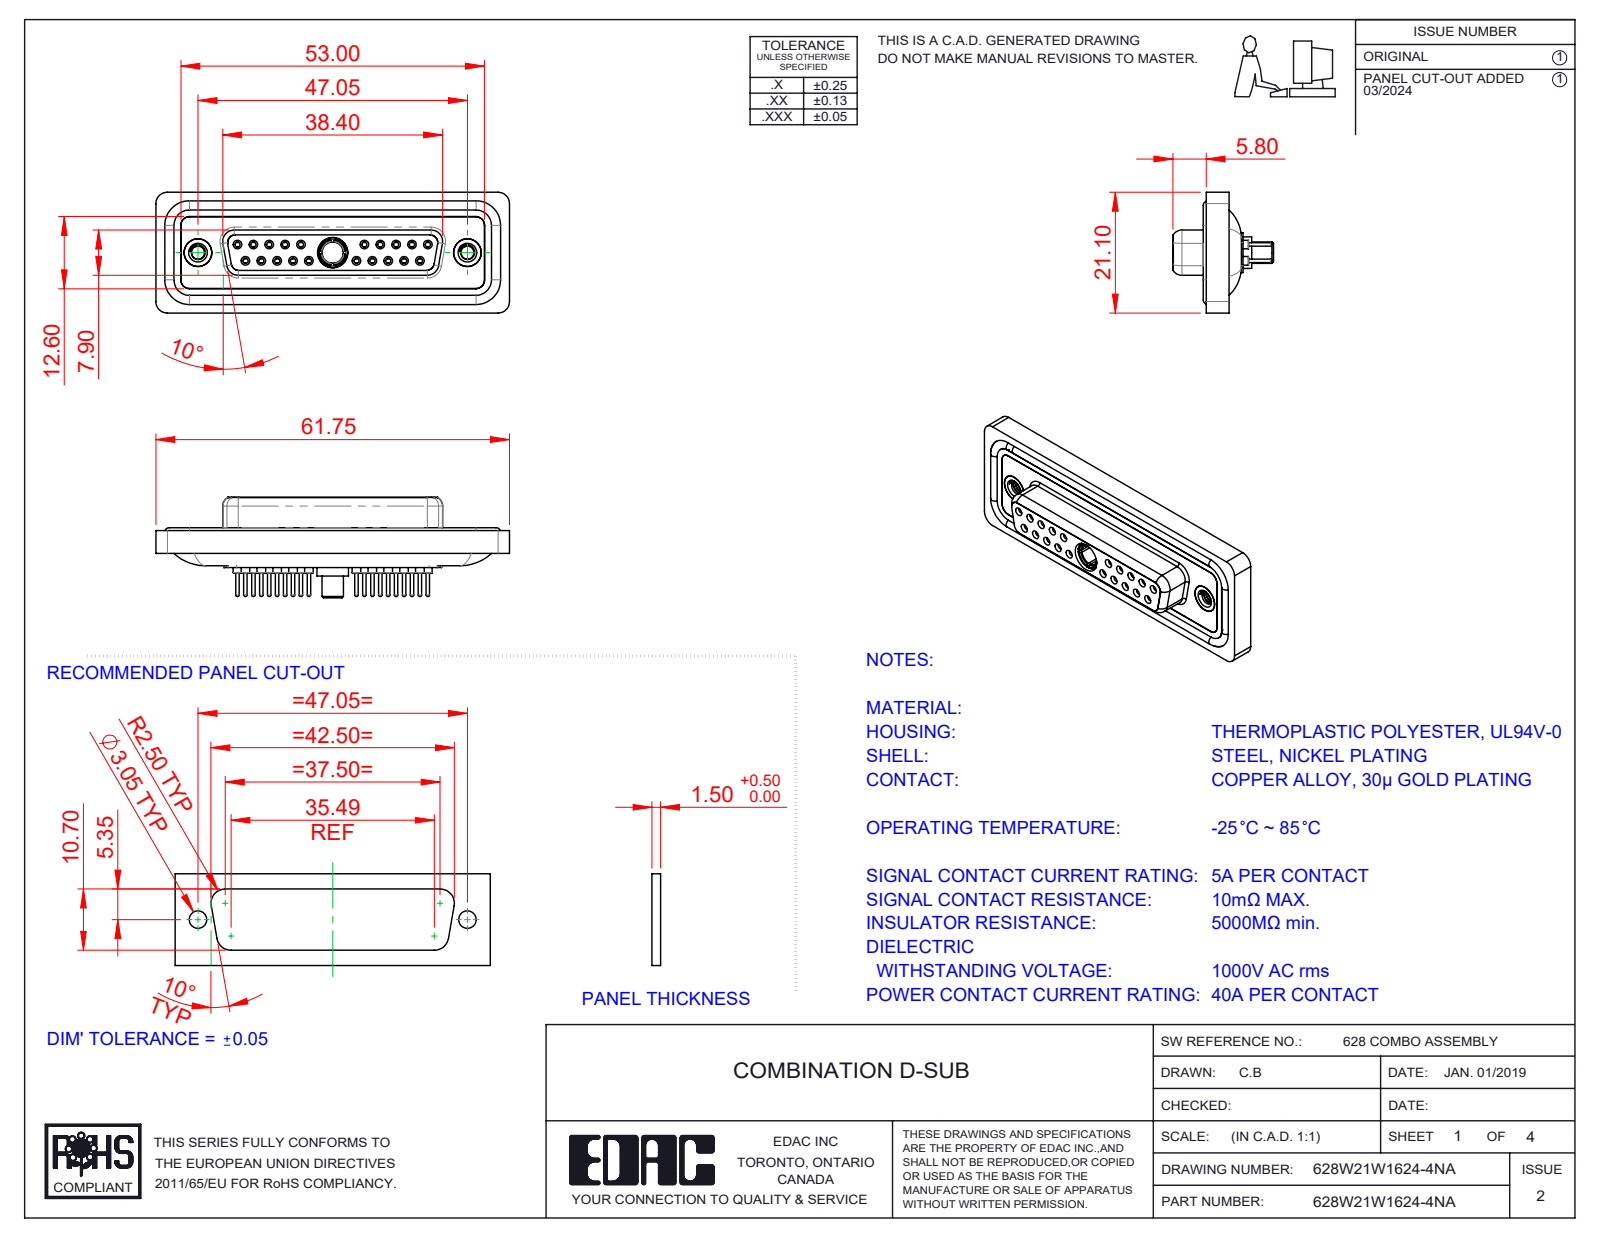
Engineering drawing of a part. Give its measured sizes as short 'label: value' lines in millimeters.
name: 628Combo Threaded Rivet_A; 628Combo Contact Row 2_24; 628Combo Housing_21W1; 628Combo Contact Row 1_24 (+5 more)
written by: SolidWorks 2023 (CONFIG_CONTROL_DESIGN)
unit: mm
bodies: 29 solids, 1558 faces (434 planar, 593 cylindrical, 531 other)
size: 61.75 × 21.1 × 17.55
volume: 8 394 mm³; area: 14 010 mm²
holes: 20× ⌀0.9, 20× ⌀1.1, 20× ⌀1.5, 20× ⌀2, 10× ⌀1.6, 10× ⌀1.7, 3× ⌀4.85, 2× ⌀2.26, 2× ⌀4, 2× ⌀4.05, 2× ⌀5, 1× ⌀3.7
bosses: 20× ⌀2.2, 20× ⌀0.6, 14× ⌀1.6, 2× ⌀4.95, 2× ⌀4.8, 1× ⌀5.5, 1× ⌀5.2, 1× ⌀4.96
rounds: 22× R1.5, 18× R2, 8× R1.35, 8× R1.6, 4× R0.25, 4× R0.5, 4× R0.6, 4× R0.65
face distances: 0.4, 1.8, 7.45, 6.6, 5.65, 0.5, 1.6, 7.05, 2.9, 1.1
hole spacings: 3.16, 2.77, 5.54, 5.03, 8.31, 7.48, 16.62, 19.39
